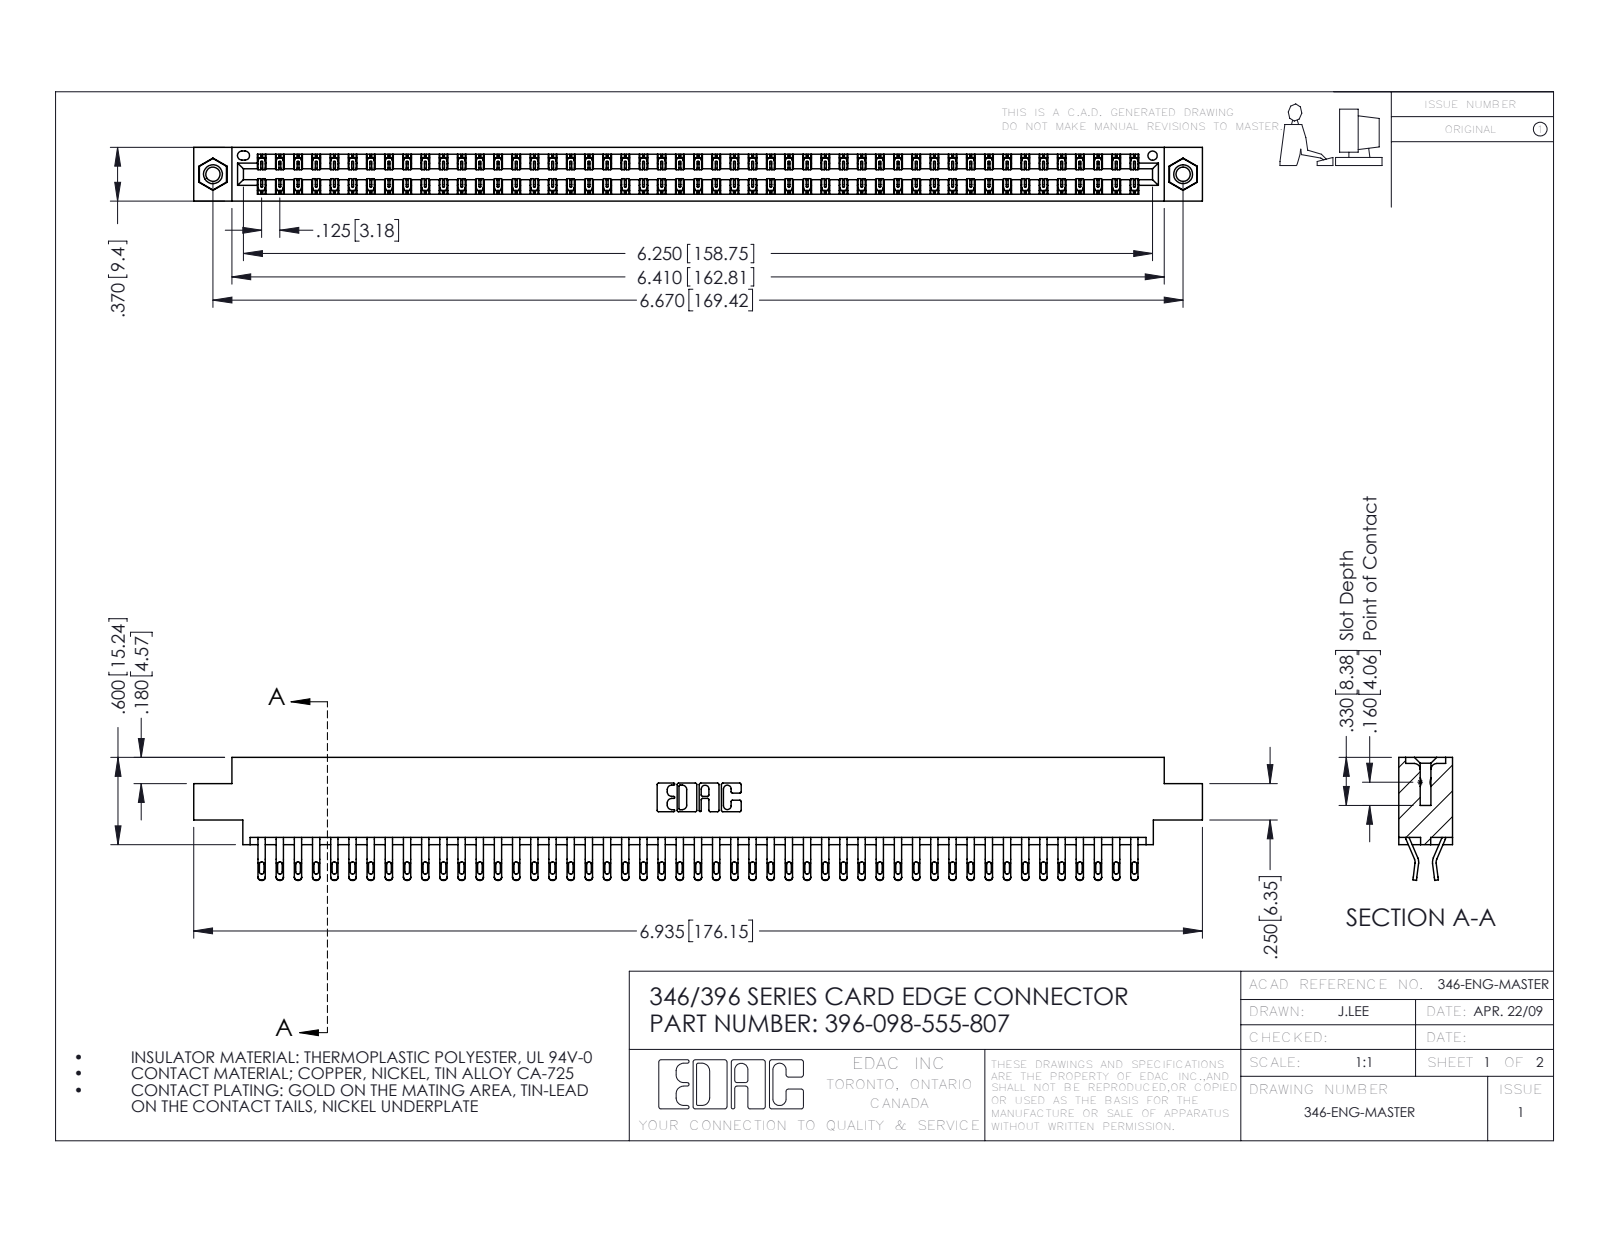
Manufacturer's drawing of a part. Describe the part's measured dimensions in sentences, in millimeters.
The part is named "346 Part_0.170 Offset - 0.156 Dia-TI; 396-098-555-807; 345-292-001_555 Tail; 345-250-001_345-250-005-103". Its 3-D file was written by "SolidWorks 2016 (CONFIG_CONTROL_DESIGN)". It is 101 solids with 5870 faces: 3346 planar, 2508 cylindrical and 16 other. Overall it measures 176.1 by 21.5 by 9.4 millimeters. Its volume is 17 350 cubic millimeters and its surface area 25 180 square millimeters. Round holes: 2 of diameter 2.5, 2 of diameter 3.2, 2 of diameter 4, 1 of diameter 1.6. Round bosses or shafts: 2 of diameter 3.9. Partial cylindrical surfaces (rounded edges, fillets, slot ends): 196 of radius 0.4, 196 of radius 0.5, 147 of radius 0.2, 22 of radius 0.3, 6 of radius 0.2, 6 of radius 0.8, 3 of radius 0.7, 2 of radius 0.3. The main face-to-face distances are 1.2, 8.2, 9.4, 6.4, 0.6, 1.8, 7.6, 7, 5.6, 3.8. The hole center spacings are 6.2, 164.1, 169.4.
